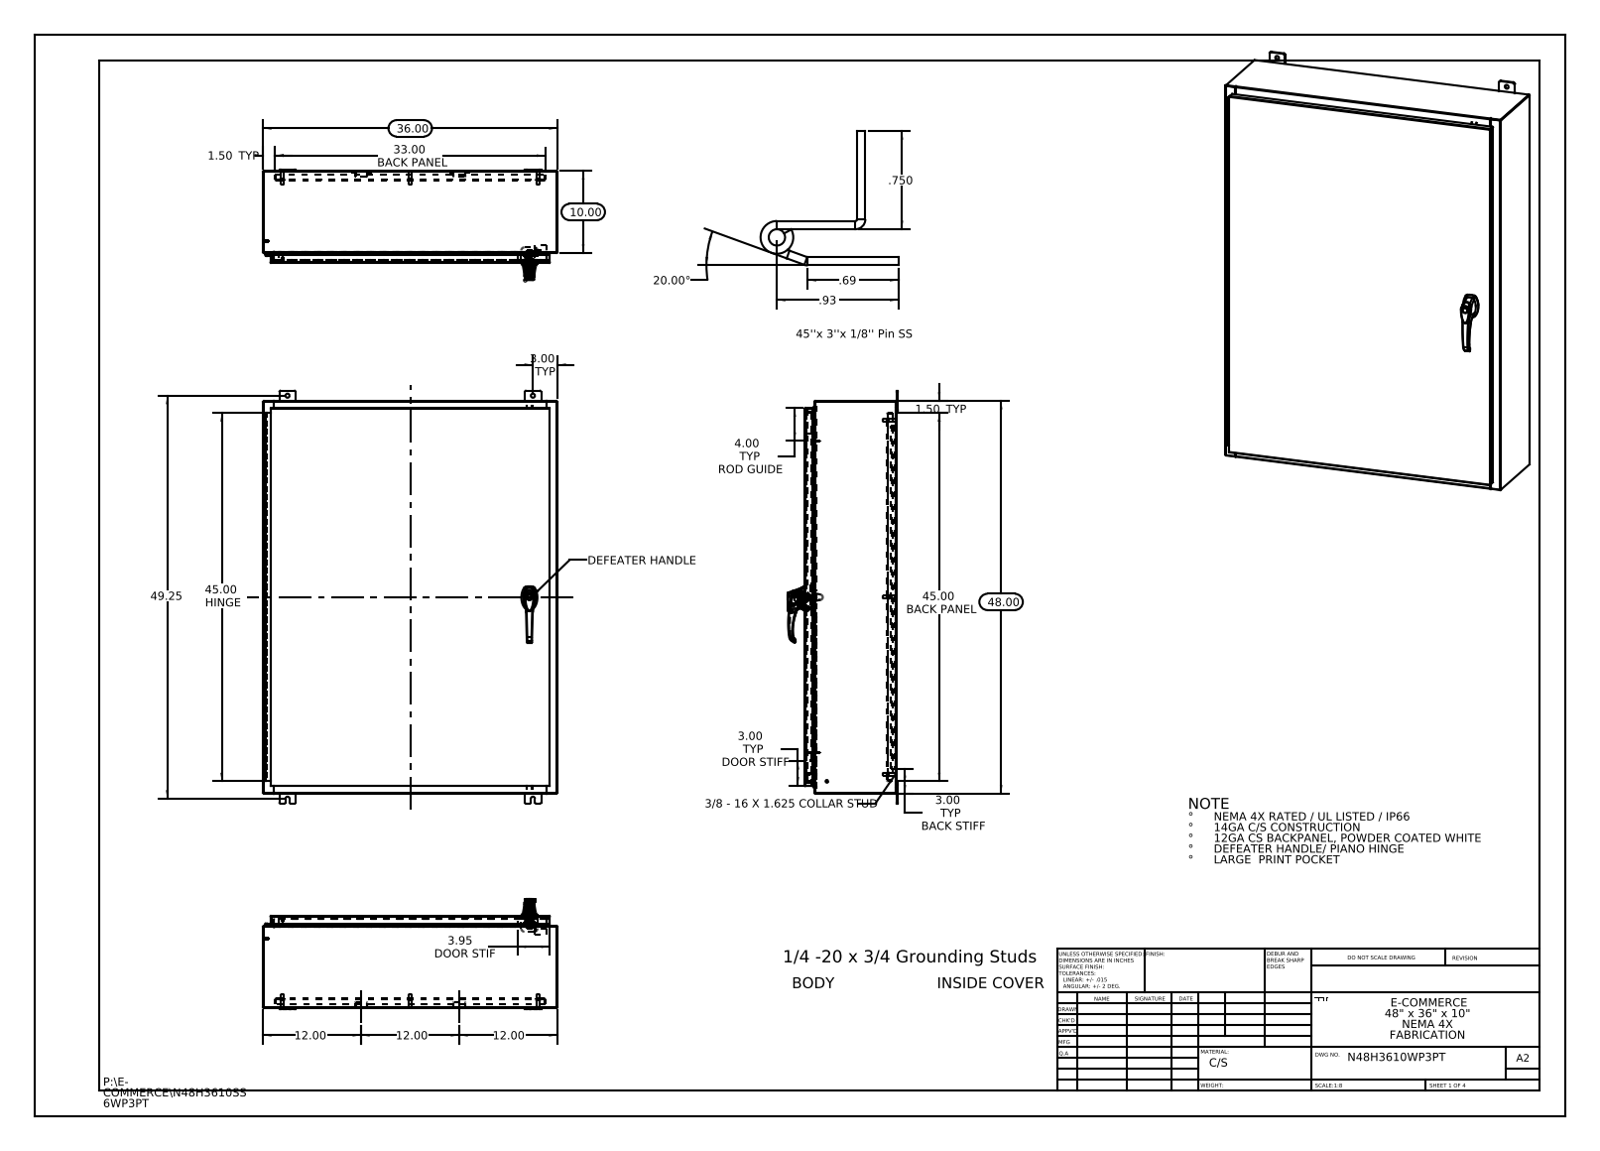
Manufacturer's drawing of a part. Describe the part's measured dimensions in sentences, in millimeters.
The part is named "10_30 CD Stud; 2616310101; 297026; N48H3610SS6WP3PT Top (+8 more)". Its 3-D file was written by "SolidWorks 2013 (CONFIG_CONTROL_DESIGN)". It is 51 solids with 3400 faces: 1309 planar, 1305 cylindrical and 786 other. Overall it measures 1282.7 by 914.4 by 342.8 millimeters. Its volume is 10 340 000 cubic millimeters and its surface area 10 090 000 square millimeters. Round holes: 12 of diameter 12.7, 10 of diameter 6.4, 3 of diameter 3.5, 3 of diameter 4.1, 2 of diameter 2, 2 of diameter 5.2, 2 of diameter 8, 2 of diameter 11.1, 1 of diameter 3.2, 1 of diameter 3.2, 1 of diameter 5, 1 of diameter 7. Round bosses or shafts: 10 of diameter 4, 10 of diameter 3.6, 8 of diameter 15.9, 8 of diameter 9.5, 8 of diameter 8.4, 3 of diameter 8, 3 of diameter 6, 1 of diameter 30. Partial cylindrical surfaces (rounded edges, fillets, slot ends): 37 of radius 3, 34 of radius 0.3, 33 of radius 0.2, 28 of radius 2.2, 24 of radius 4.8, 15 of radius 1, 12 of radius 0.7, 6 of radius 0.2. The main face-to-face distances are 1.9, 282.6, 280.7, 284.5, 2.6, 25.4, 257.2, 27.3, 255.3, 29.9. The hole center spacings are 440.9, 499.5, 549.3, 965.3, 1168, 793.8, 1098.6, 7.5.
